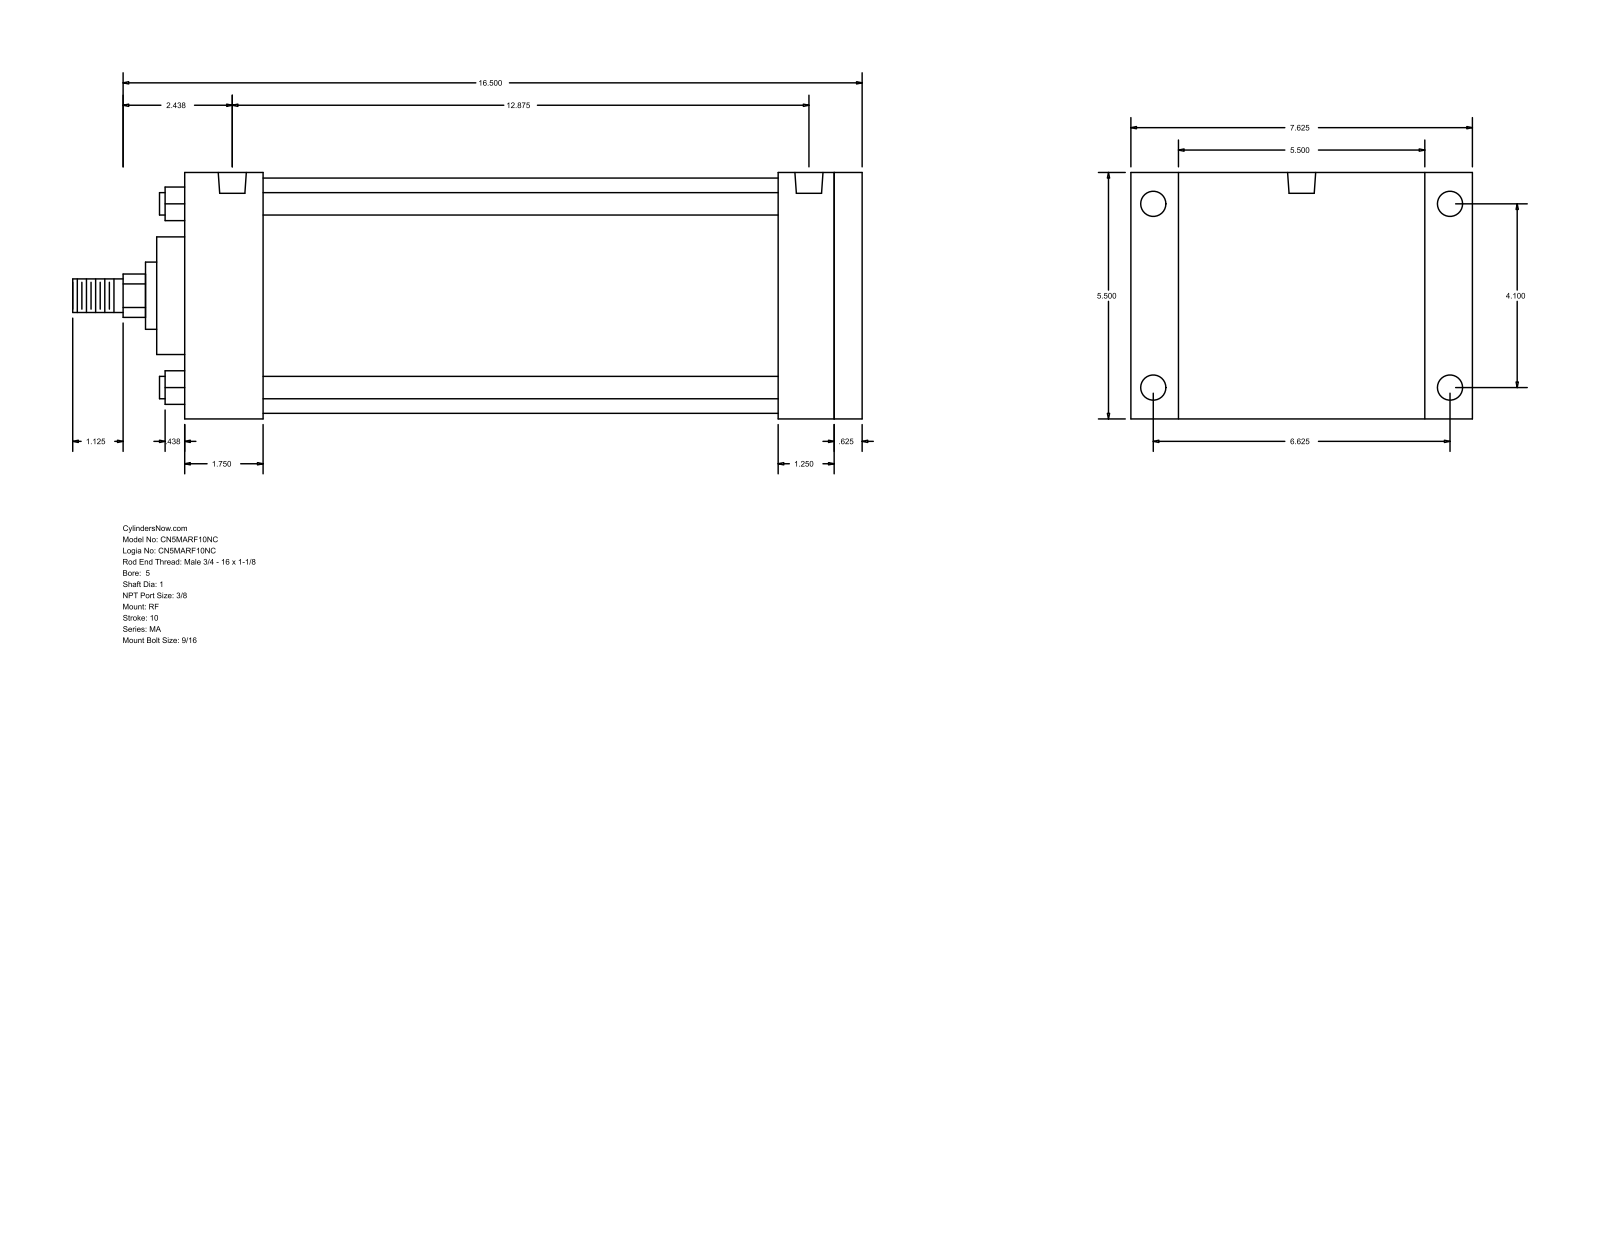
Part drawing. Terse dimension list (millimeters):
name: MA_RF__0500_1
written by: GSSL Pune (CONFIG_CONTROL_DESIGN)
unit: mm
bodies: 0 solids, 94 faces (65 planar, 29 cylindrical, 0 other)
size: 447.68 × 193.68 × 139.7
holes: 4× ⌀11.11, 4× ⌀14.29, 2× ⌀15.93
bosses: 4× ⌀12.7, 1× ⌀133.35, 1× ⌀66.67, 1× ⌀38.1, 1× ⌀25.4, 1× ⌀19.05
rounds: 1× R12.29
face distances: 139.7, 384.18, 15.87, 368.31, 47.62, 44.46, 323.85, 339.72, 336.56, 292.1
hole spacings: 4.76, 104.14, 168.28, 197.9, 317.51, 322.27, 327.03
